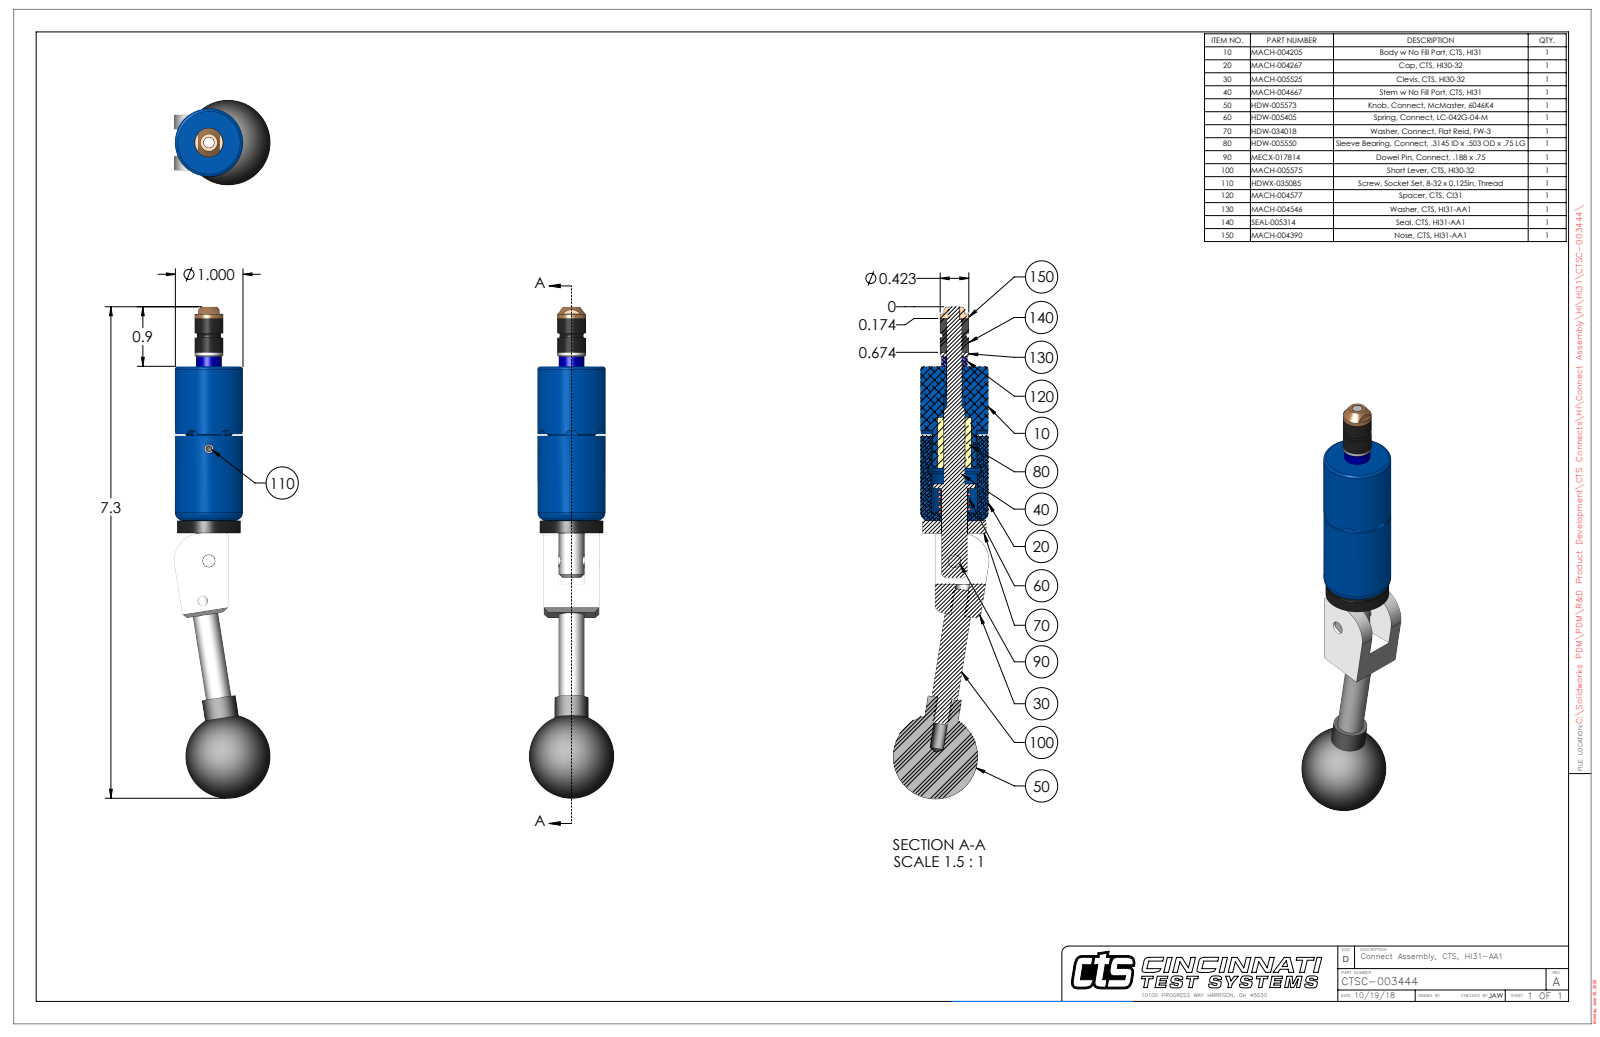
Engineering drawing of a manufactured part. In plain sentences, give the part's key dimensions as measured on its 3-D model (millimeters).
The part is named "CTSC-003444". Its 3-D file was written by "SolidWorks 2023 (AUTOMOTIVE_DESIGN)". It is 10 solids with 254 faces: 98 planar, 99 cylindrical and 57 other. Overall it measures 184.6 by 36 by 31.8 millimeters. Its volume is 61 680 cubic millimeters and its surface area 19 740 square millimeters. Round holes: 2 of diameter 5.1, 1 of diameter 3.5, 1 of diameter 3.8, 1 of diameter 4, 1 of diameter 4.8, 1 of diameter 5.5, 1 of diameter 5.8, 1 of diameter 5.8, 1 of diameter 9.8, 1 of diameter 10. Round bosses or shafts: 1 of diameter 25.4, 1 of diameter 23.8, 1 of diameter 12.7, 1 of diameter 10.7, 1 of diameter 9.7, 1 of diameter 9.6, 1 of diameter 9.5, 1 of diameter 6.4. Partial cylindrical surfaces (rounded edges, fillets, slot ends): 6 of radius 2.4, 2 of radius 0.7, 1 of radius 8.7, 1 of radius 10.2, 1 of radius 11.9. The main face-to-face distances are 5.3, 15.3, 20.6, 4.7, 57.9, 62.6, 9.9, 26, 31.8, 36.6. The hole center spacings are 15.2, 42.1, 57.2.
